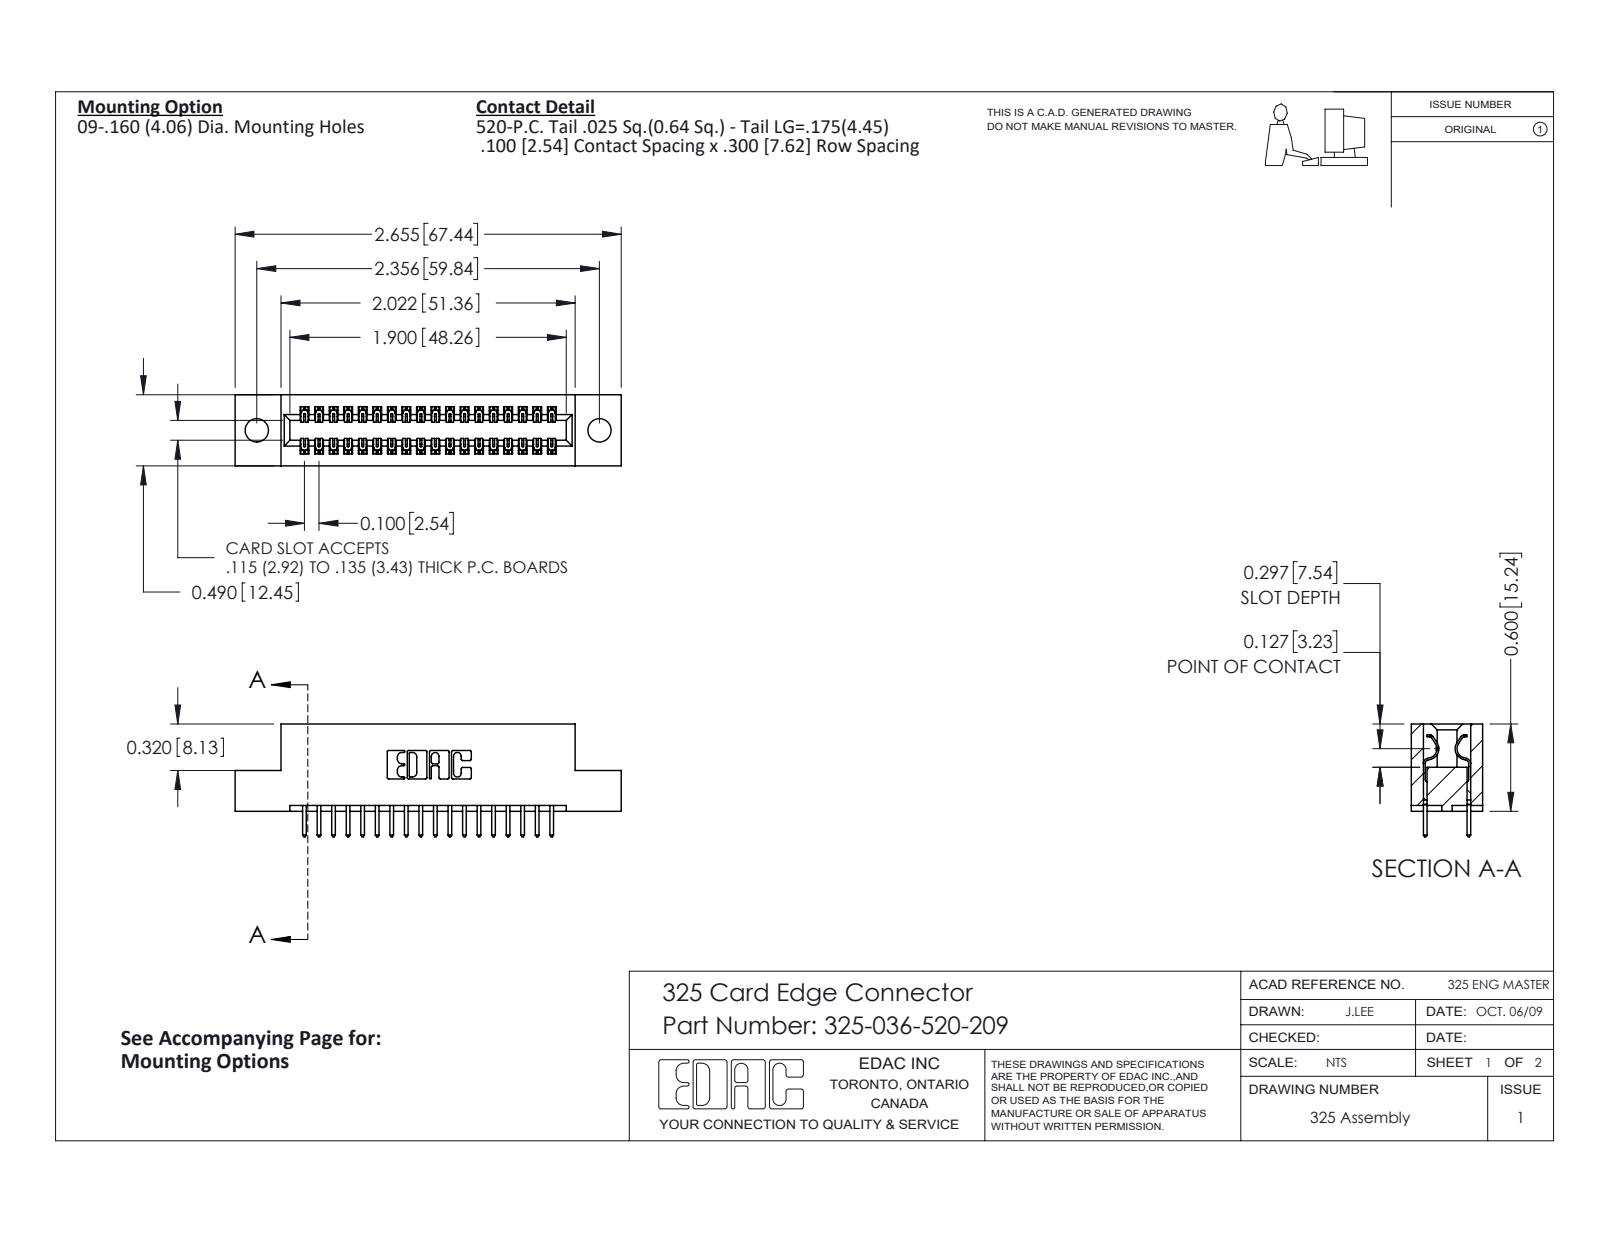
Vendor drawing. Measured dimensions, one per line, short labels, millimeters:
name: 325-292-001_325-293-120; 325 Part_.160 TH; 325-036-520-209
written by: SolidWorks 2016 (CONFIG_CONTROL_DESIGN)
unit: mm
bodies: 37 solids, 1986 faces (1366 planar, 620 cylindrical, 0 other)
size: 67.4 × 19.7 × 12.4
volume: 8 260 mm³; area: 9 271 mm²
holes: 2× ⌀4.1
rounds: 54× R0.2, 36× R0.3, 22× R0.3, 6× R0.2, 6× R0.8, 3× R0.7, 2× R0.4, 2× R0.6
face distances: 2.1, 10.3, 7.6, 12.4, 2.7, 9.7, 0.6, 8.3, 15.2, 5.1
hole spacings: 59.8
